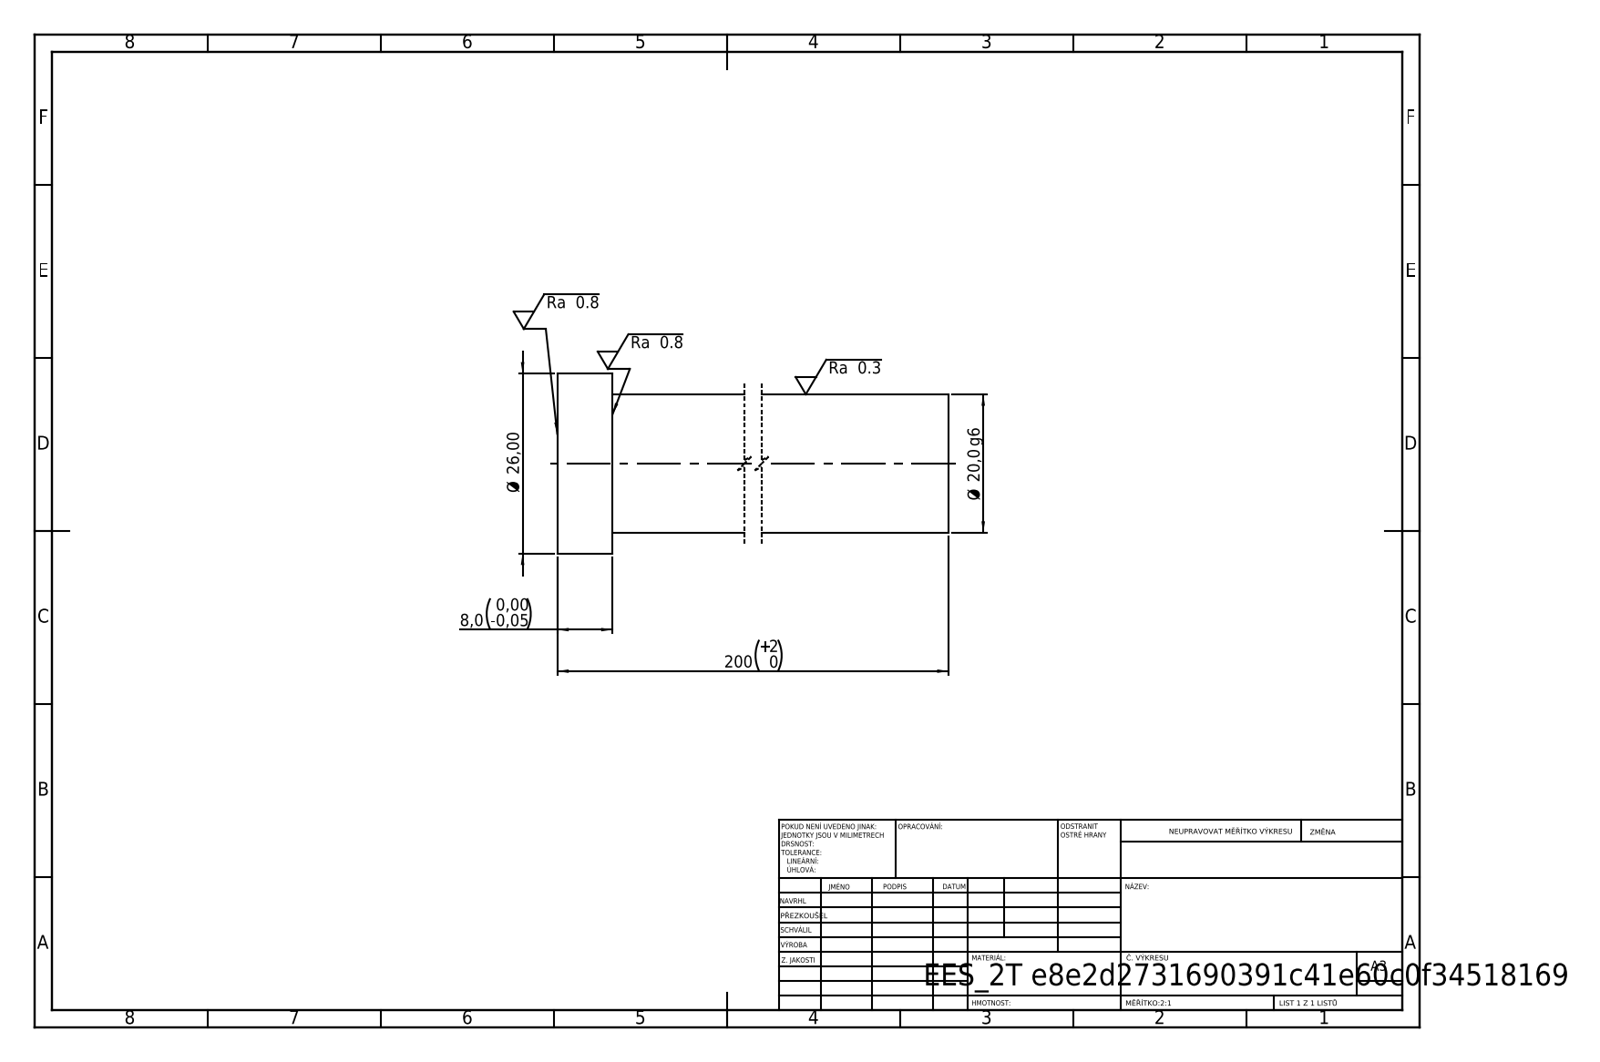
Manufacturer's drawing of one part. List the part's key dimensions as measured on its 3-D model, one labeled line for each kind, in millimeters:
STEP written by: SolidWorks 2019 (CONFIG_CONTROL_DESIGN)
Units: millimetres
Bodies: 1 solid, 7 faces (3 planar, 4 cylindrical, 0 other)
Overall size (bounding box): 200 × 26 × 26
Volume: 64 566 mm³ · Surface area: 13 779 mm²
Round bosses / shafts (diameter × count): ⌀26 ×1, ⌀20 ×1
Main face-to-face distances: 200, 8, 192
